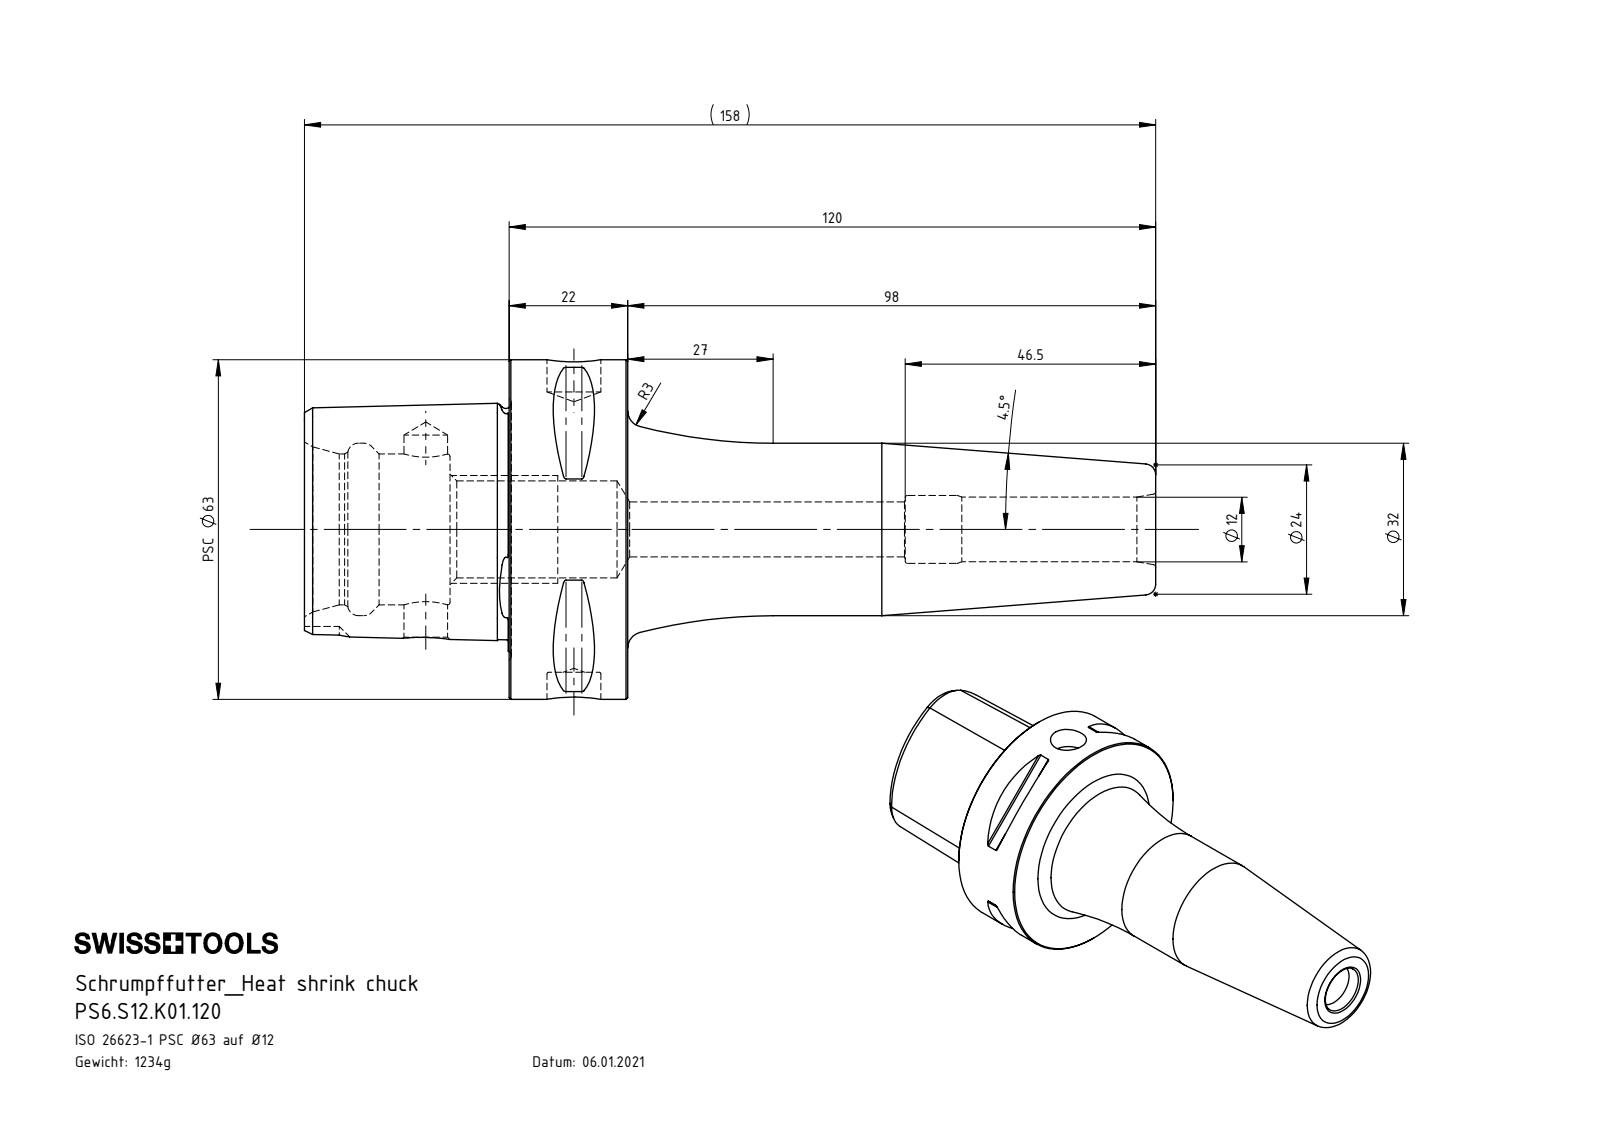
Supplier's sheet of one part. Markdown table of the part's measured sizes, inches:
| quantity | value |
| --- | --- |
| part name | PS6.S12.K01.120 |
| STEP written by | SolidWorks 2022 (AUTOMOTIVE_DESIGN) |
| units | inches |
| bodies | 1 solid, 154 faces (22 planar, 35 cylindrical, 97 other) |
| overall size | 6.22 × 2.48 × 2.48 |
| volume | 9.596 in³ |
| surface area | 50.09 in² |
| round holes (diameter × count) | 0.319 × 1, 0.394 × 1, 0.402 × 1, 0.472 × 1, 0.496 × 1, 0.709 × 1, 1.102 × 1, 1.26 × 1 |
| round bosses / shafts (diameter × count) | 2.48 × 1 |
| partial cylindrical surfaces (radius × count) | 0.02 × 8, 0.236 × 1 |
| main face-to-face distances | 0.866, 1.496, 2.362, 0.98, 1.063, 0.433, 1.299, 2.197, 6.22, 5.157 |
| hole center spacings | 1.083 |
